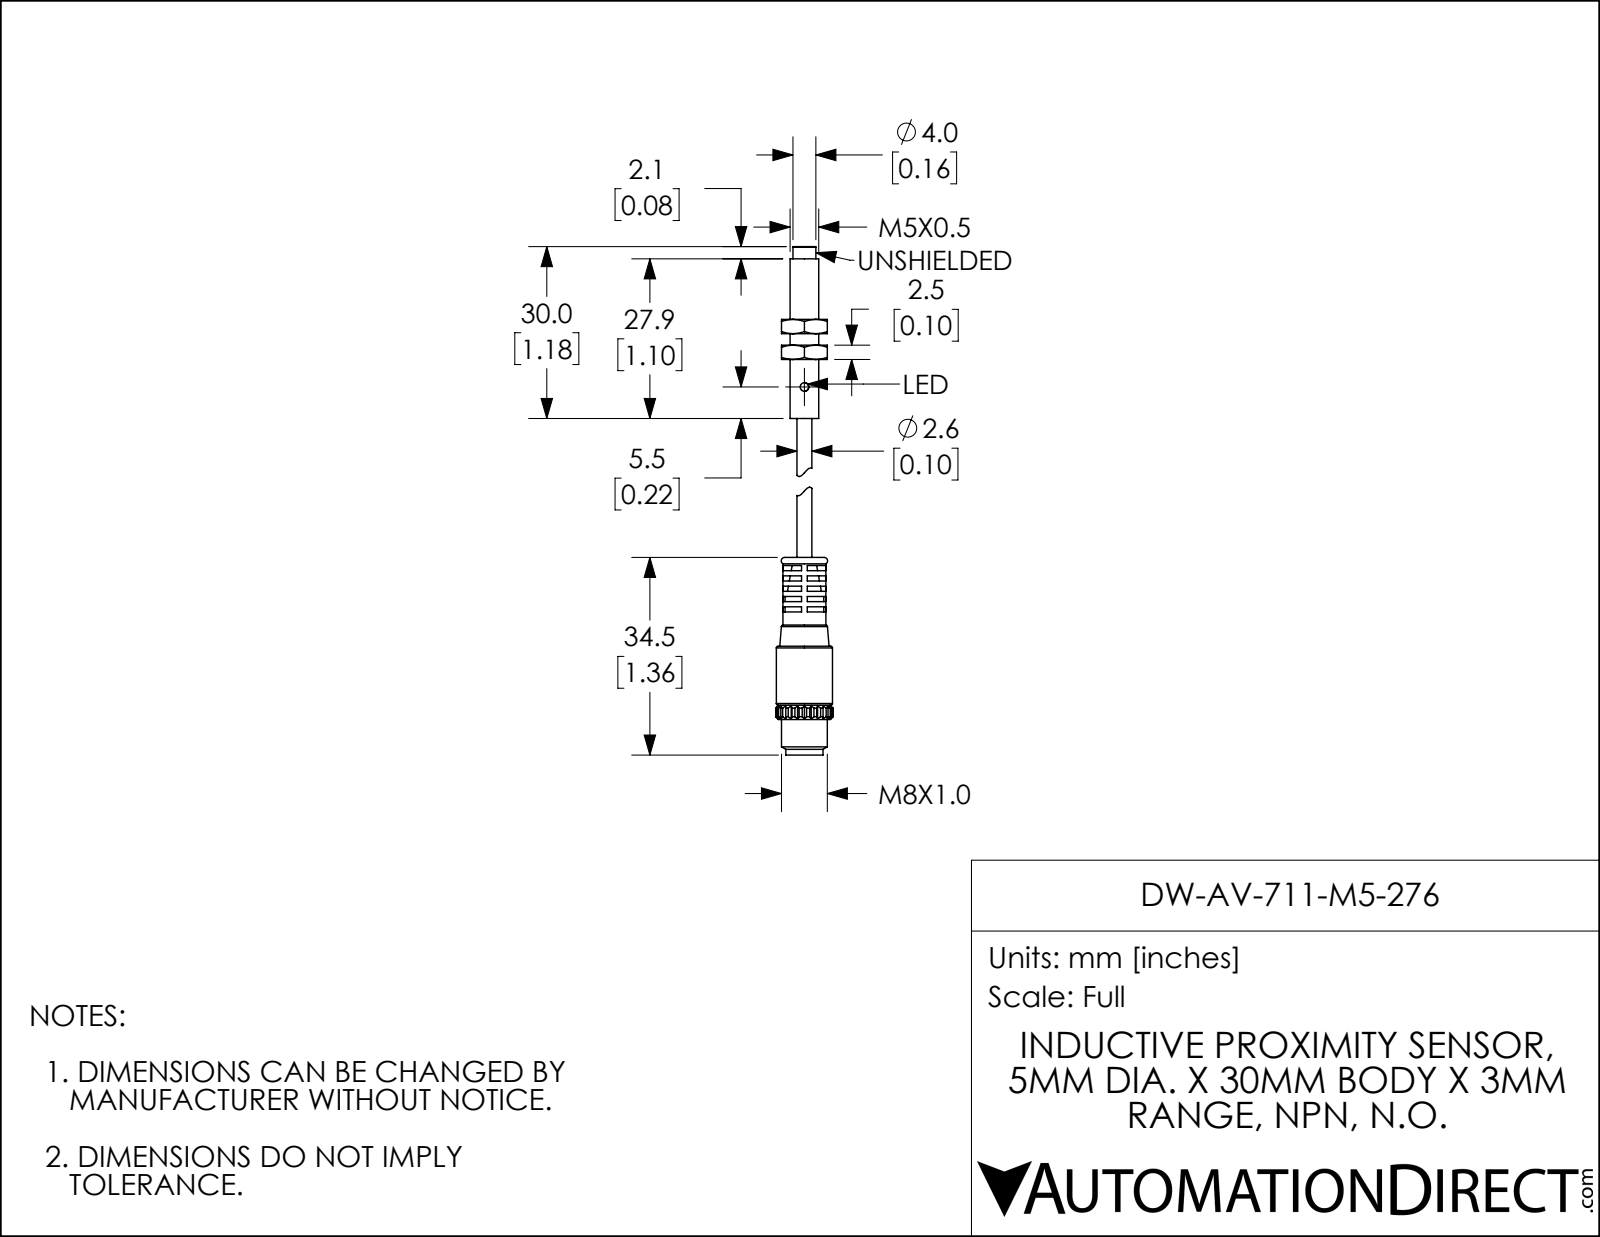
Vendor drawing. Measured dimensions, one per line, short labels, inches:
name: DW-AV-711-M5-276
written by: SolidWorks 2017 (AUTOMOTIVE_DESIGN)
unit: in
bodies: 5 solids, 217 faces (143 planar, 46 cylindrical, 28 other)
size: 3.494 × 0.393 × 0.393
volume: 0.188 in³; area: 4.393 in²
holes: 1× ⌀0.059, 1× ⌀0.228
bosses: 3× ⌀0.039, 1× ⌀0.386, 1× ⌀0.315, 1× ⌀0.295, 1× ⌀0.269, 1× ⌀0.256, 1× ⌀0.197, 1× ⌀0.157
rounds: 1× R0.09, 1× R0.197
face distances: 0.035, 0.071, 0.106, 0.142, 0.177, 1.016, 0.213, 1.161, 0.146, 0.056
